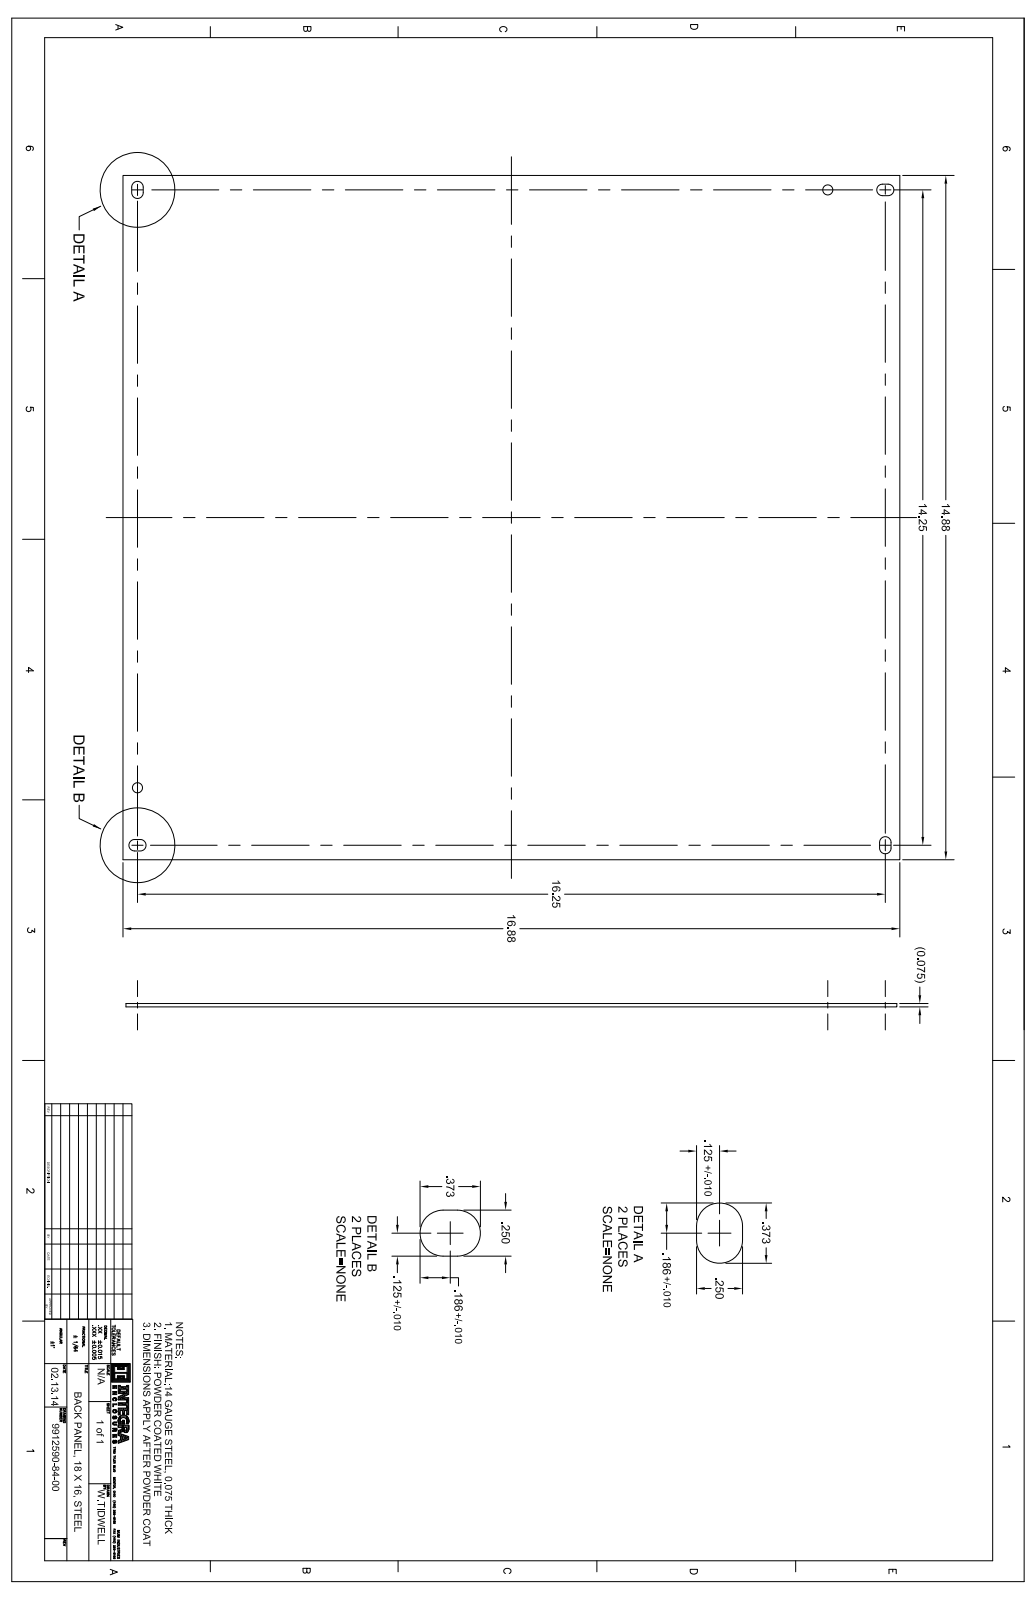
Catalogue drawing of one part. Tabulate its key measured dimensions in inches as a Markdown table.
| quantity | value |
| --- | --- |
| part name | SBP-1816-P10 |
| STEP written by | SolidWorks 2018 (AUTOMOTIVE_DESIGN) |
| units | inches |
| bodies | 1 solid, 24 faces (14 planar, 10 cylindrical, 0 other) |
| overall size | 16.88 × 14.88 × 0.075 |
| volume | 18.81 in³ |
| surface area | 506.7 in² |
| round holes (diameter × count) | 0.219 × 2 |
| partial cylindrical surfaces (radius × count) | 0.125 × 8 |
| main face-to-face distances | 0.075, 14.88, 16.88, 0.19, 0.44, 0.25, 16.44, 16.69, 16.25, 14.44 |
| hole center spacings | 19.849 |
